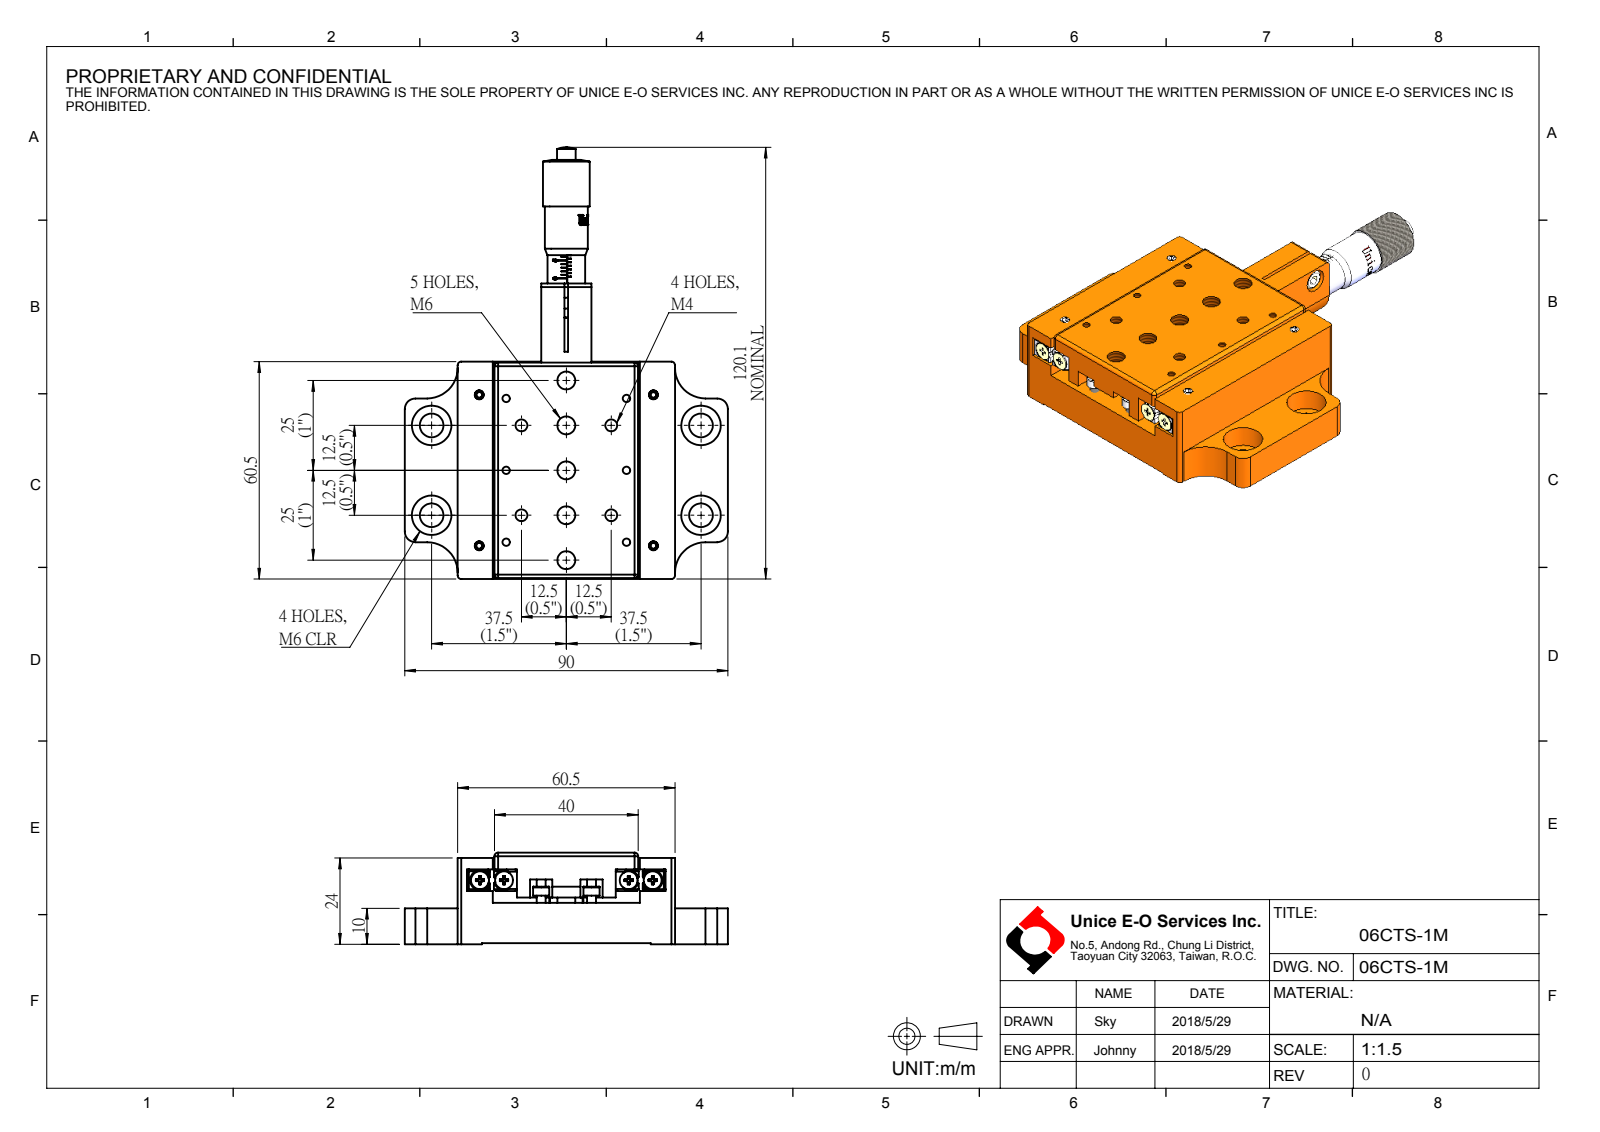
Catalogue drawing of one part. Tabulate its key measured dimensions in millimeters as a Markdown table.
| quantity | value |
| --- | --- |
| part name | 06CTS-1M |
| STEP written by | SolidWorks 2016 (AUTOMOTIVE_DESIGN) |
| units | millimeters |
| bodies | 0 solids, 613 faces (363 planar, 147 cylindrical, 103 other) |
| overall size | 120.15 × 90 × 25.5 |
| round holes (diameter × count) | 2.5 × 8, 2.05 × 6, 5 × 5, 3.3 × 4, 6.6 × 4, 11 × 4, 6.5 × 1, 8 × 1, 9.5 × 1, 10.6 × 1 |
| round bosses / shafts (diameter × count) | 5 × 5, 4.5 × 2, 2.5 × 2, 13 × 1, 12 × 1, 10.5 × 1, 9.2 × 1, 5.2 × 1 |
| partial cylindrical surfaces (radius × count) | 1 × 13, 3 × 4, 8.5 × 4, 5.98 × 1, 7 × 1 |
| main face-to-face distances | 14, 6, 1.5, 11.2, 11.5, 25.2, 25.5, 3.2, 12.5, 7.5 |
| hole center spacings | 25, 39.53, 12.5, 17.68, 35.36, 37.5, 50, 7.57 |
